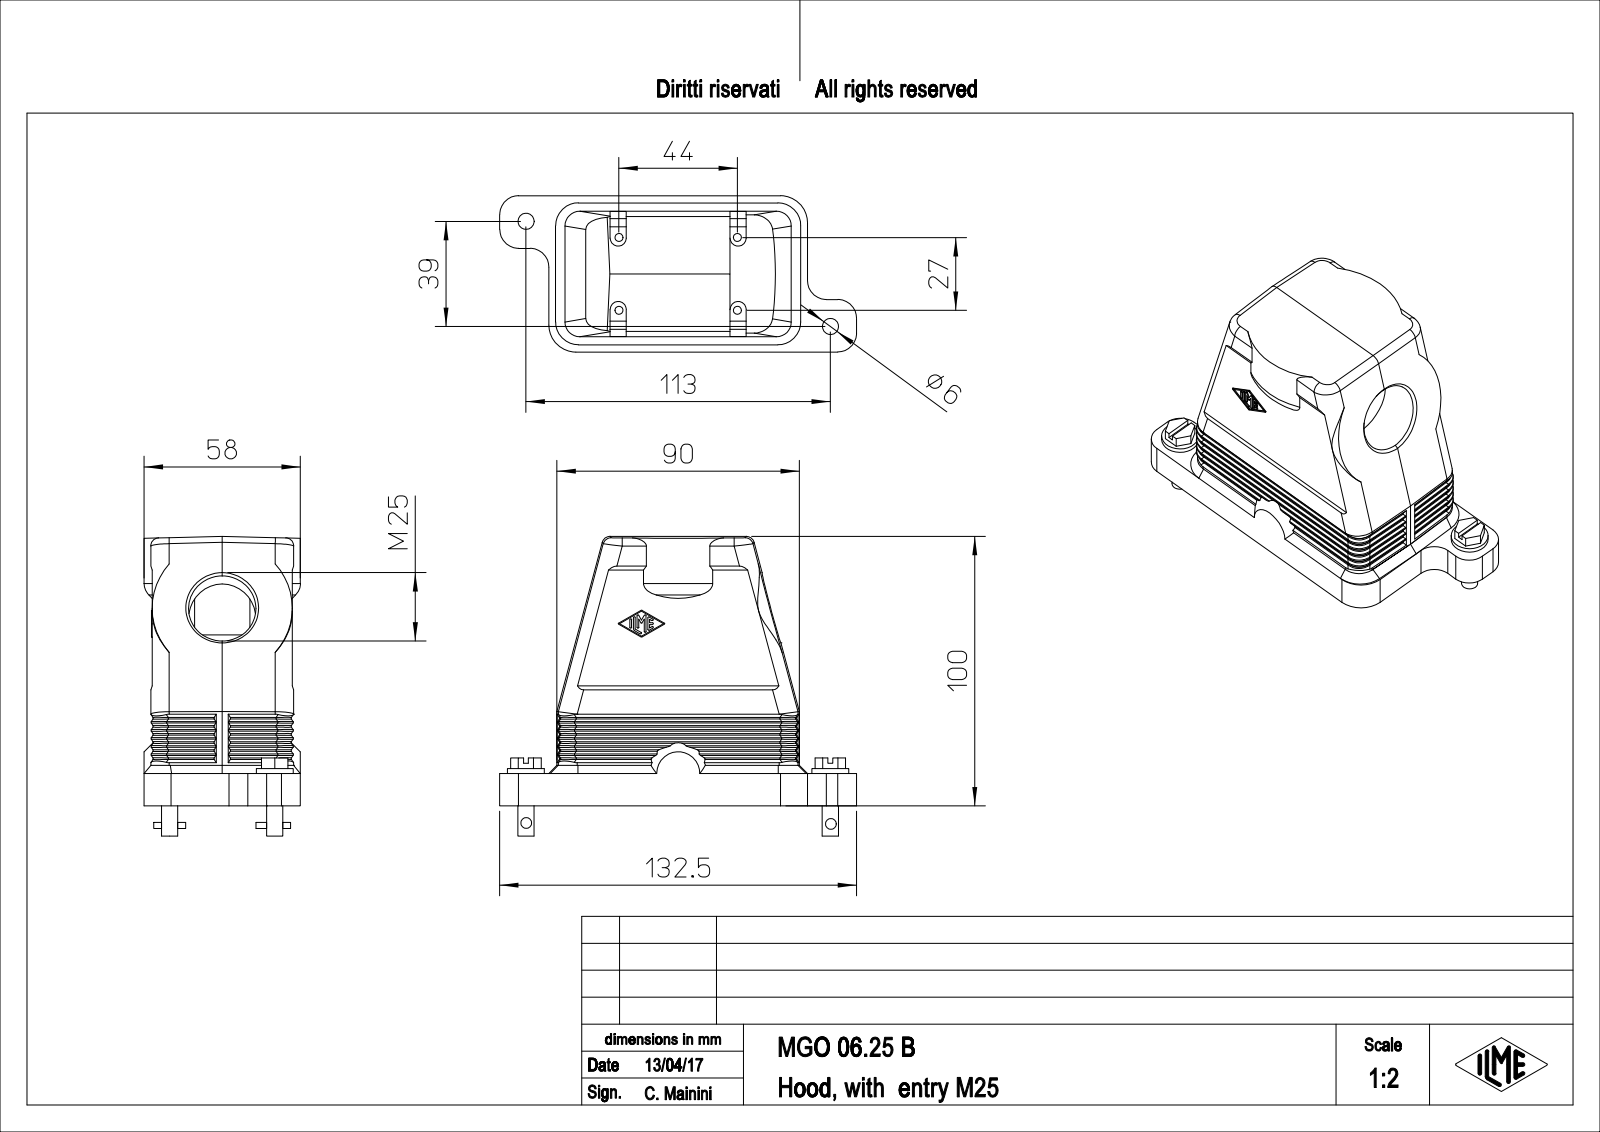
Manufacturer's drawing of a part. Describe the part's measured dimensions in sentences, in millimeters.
The part is named "MGO_06.25_B". Its 3-D file was written by "PTC Creo Elements/Direct Modeling 19.0E 27-Jun-2016 (C) Parametric Technology GmbH (AUTOMOTIVE_DESIGN)". It is 1 solid with 523 faces: 249 planar, 210 cylindrical and 64 other. Overall it measures 132.5 by 111.2 by 58 millimeters. Its volume is 146 617 cubic millimeters and its surface area 63 620 square millimeters. Round holes: 4 of diameter 3, 1 of diameter 25. Round bosses or shafts: 2 of diameter 13.7, 2 of diameter 6, 2 of diameter 2. Partial cylindrical surfaces (rounded edges, fillets, slot ends): 66 of radius 0.5, 62 of radius 7, 15 of radius 0.33, 6 of radius 3, 4 of radius 5.5, 4 of radius 8.5, 3 of radius 0.17, 2 of radius 10. The main face-to-face distances are 3, 55, 52, 2.5, 6, 44.5, 3.33, 0.5, 55.5, 52.5. The hole center spacings are 27, 44, 51.62.
